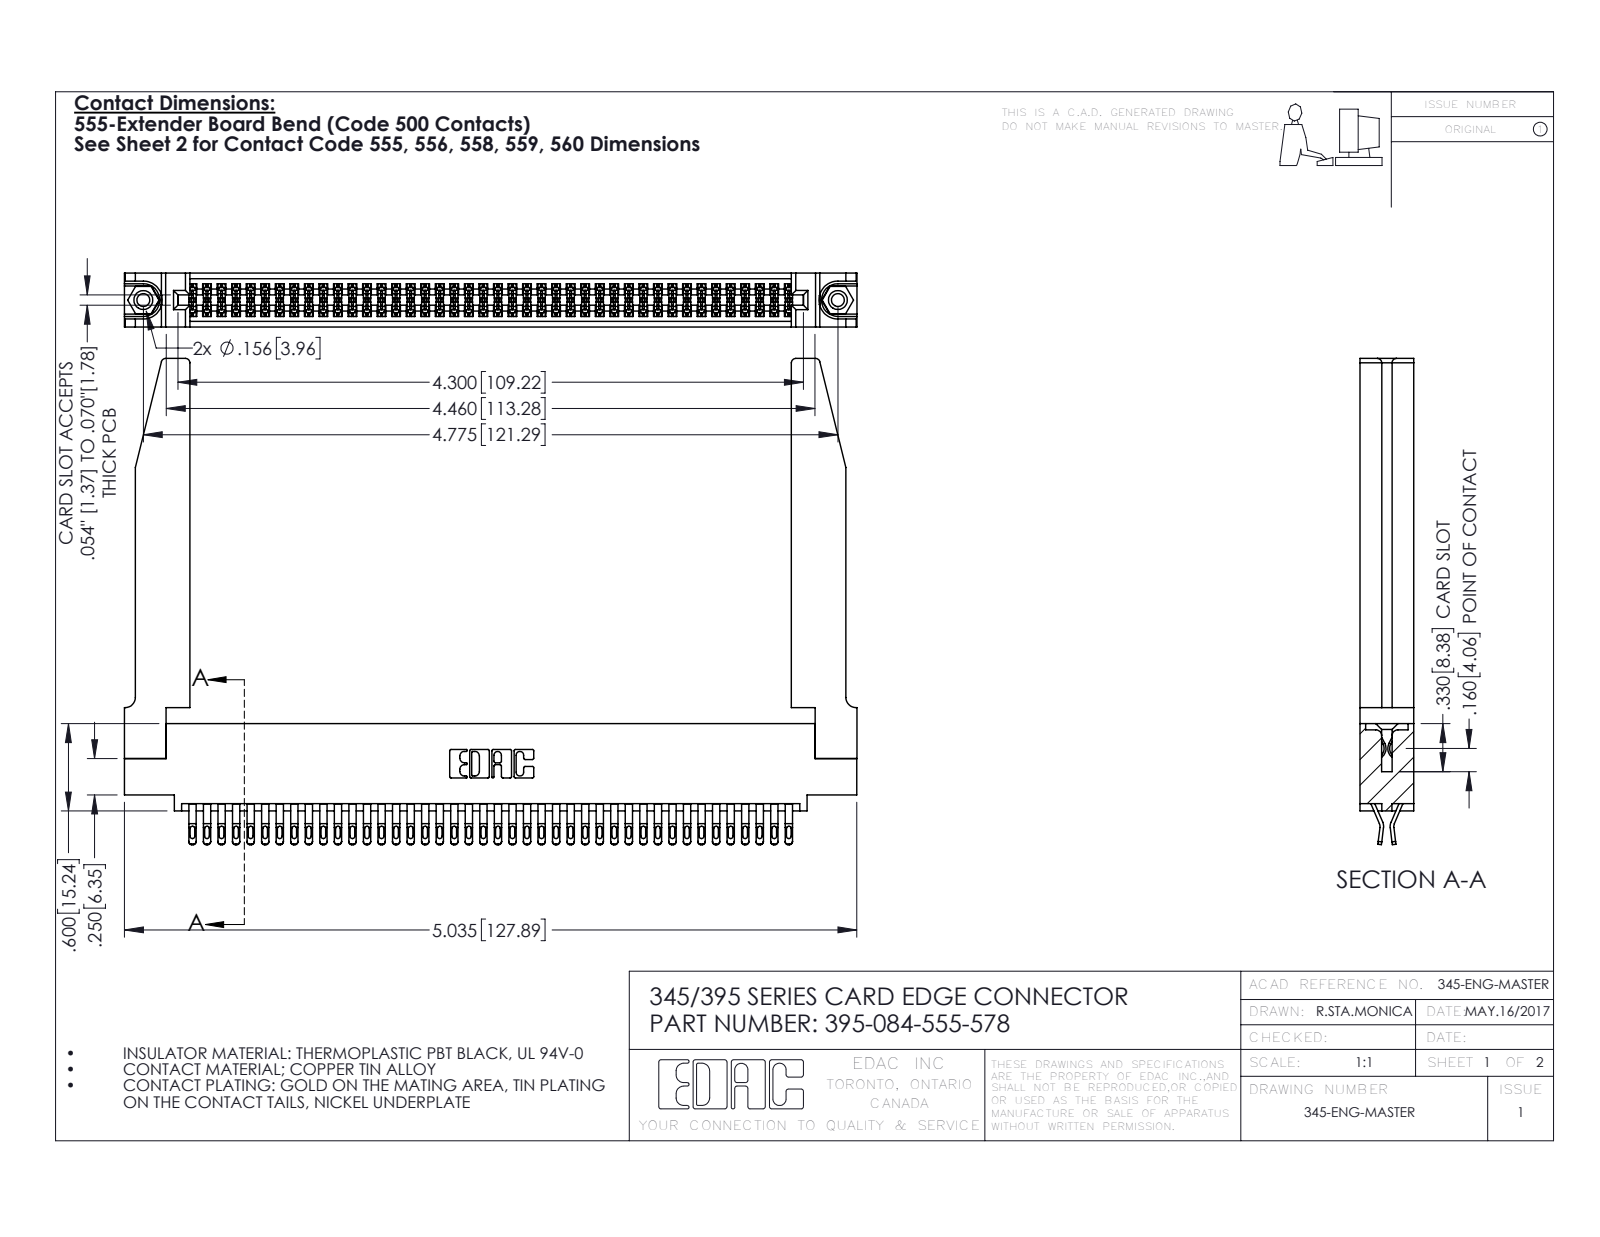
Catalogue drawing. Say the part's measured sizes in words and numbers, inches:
The part is named "345 Part_0.110 Offset - 0.156 Dia-TH; 345-250-001_345-250-001-102; 395-084-555-578; 345-292-001_555 Tail (+1 more)". Its 3-D file was written by "SolidWorks 2016 (CONFIG_CONTROL_DESIGN)". It is 89 solids with 5068 faces: 2830 planar, 2186 cylindrical and 52 other. Overall it measures 5.036 by 3.342 by 0.37 inches. Its volume is 1.243 cubic inches and its surface area 40.92 square inches. Round holes: 2 of diameter 0.089, 2 of diameter 0.125, 2 of diameter 0.156, 1 of diameter 0.064. Round bosses or shafts: 2 of diameter 0.155. Partial cylindrical surfaces (rounded edges, fillets, slot ends): 210 of radius 0.016, 168 of radius 0.02, 126 of radius 0.006, 22 of radius 0.01, 8 of radius 0.03, 6 of radius 0.007, 6 of radius 0.031, 3 of radius 0.026. The main face-to-face distances are 0.37, 0.072, 0.298, 0.025, 0.2, 0.098, 0.272, 0.225, 0.148, 0.15. The hole center spacings are 0.27, 4.539, 4.775.
